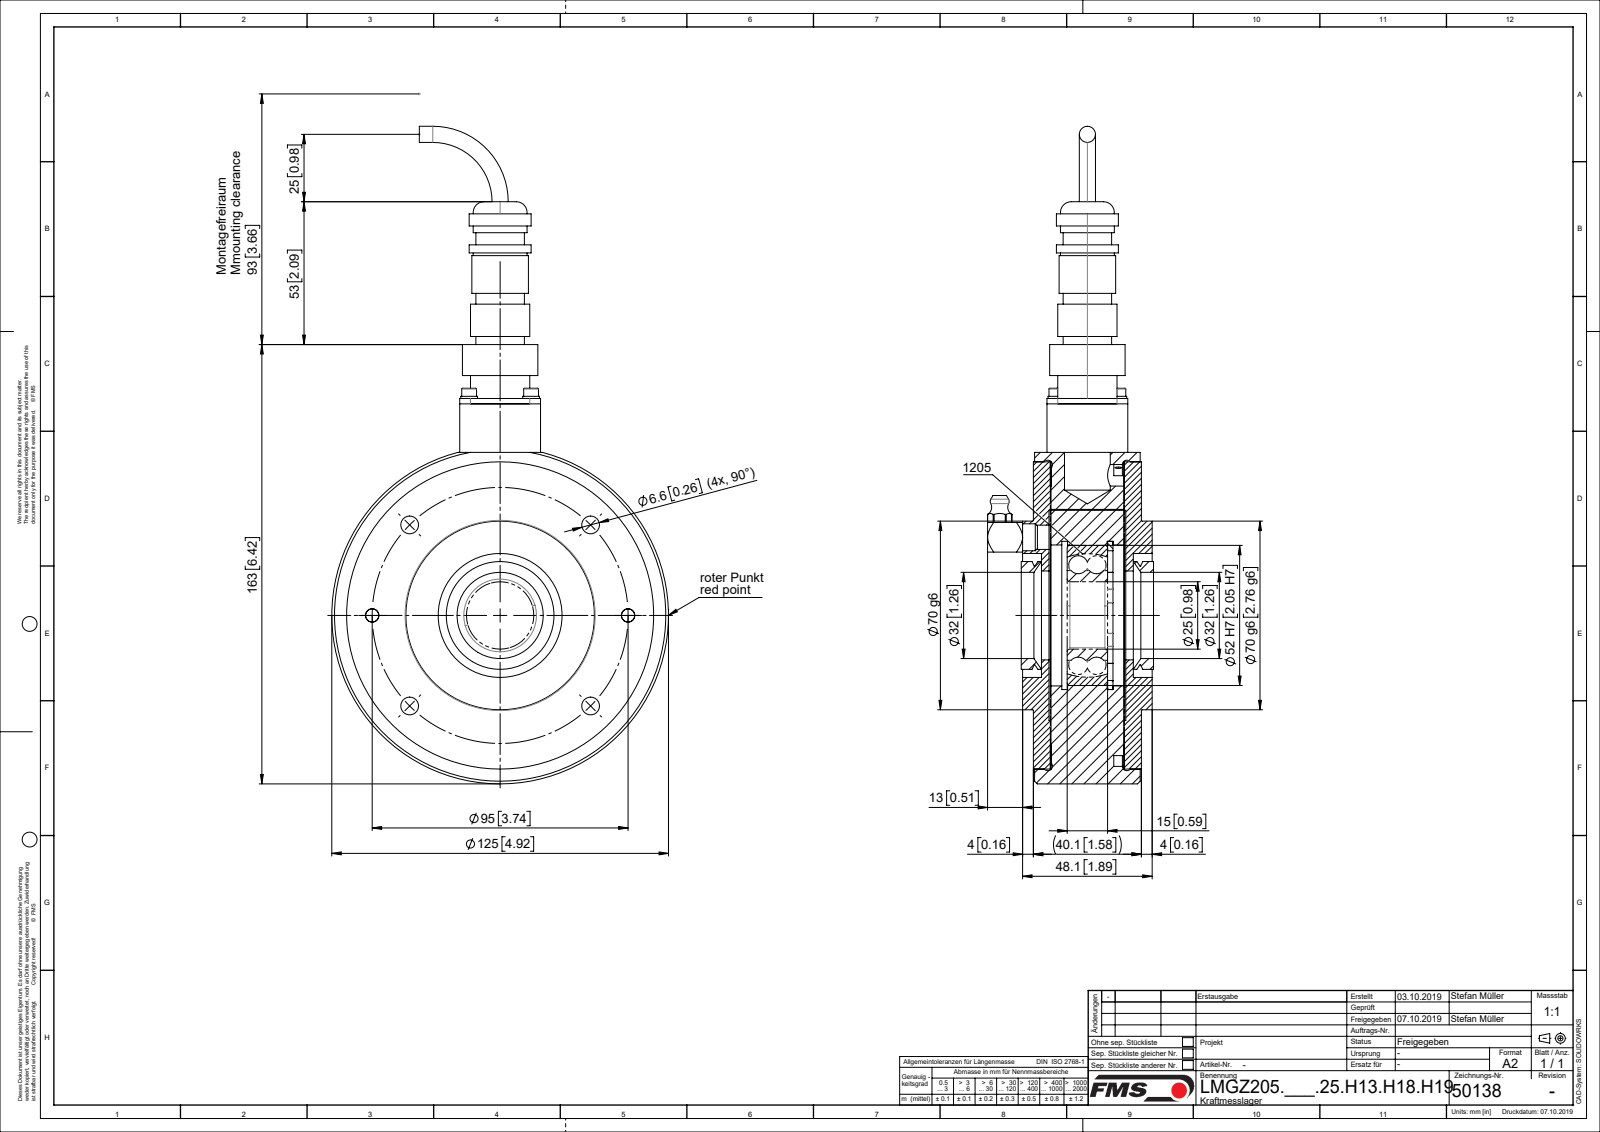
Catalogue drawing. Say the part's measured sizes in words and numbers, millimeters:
The part is named "L50138; L4832404; L48965; TEIL1 (+8 more)". Its 3-D file was written by "Mechanical Desktop 2007 (CONFIG_CONTROL_DESIGN)". It is 22 solids with 439 faces: 109 planar, 258 cylindrical and 72 other. Overall it measures 243.5 by 125 by 63.1 millimeters. Its volume is 491 950 cubic millimeters and its surface area 148 109 square millimeters. Round holes: 6 of diameter 6.6, 4 of diameter 2.6, 4 of diameter 3.2, 4 of diameter 3.4, 2 of diameter 5, 2 of diameter 11, 1 of diameter 8.91, 1 of diameter 25, 1 of diameter 31, 1 of diameter 33, 1 of diameter 37.9, 1 of diameter 46. Round bosses or shafts: 4 of diameter 6.2, 4 of diameter 5.5, 4 of diameter 3, 4 of diameter 2.5, 3 of diameter 10, 3 of diameter 6, 1 of diameter 125, 1 of diameter 114. Partial cylindrical surfaces (rounded edges, fillets, slot ends): 8 of radius 5, 4 of radius 4, 1 of radius 40.5, 1 of radius 47. The main face-to-face distances are 27.25, 33.55, 6.3, 6.55, 33.8, 27, 27.5, 40.1, 4, 10.55. The hole center spacings are 47.5, 23, 36.36, 67.18, 87.77, 32.53, 33.9, 55.65.
